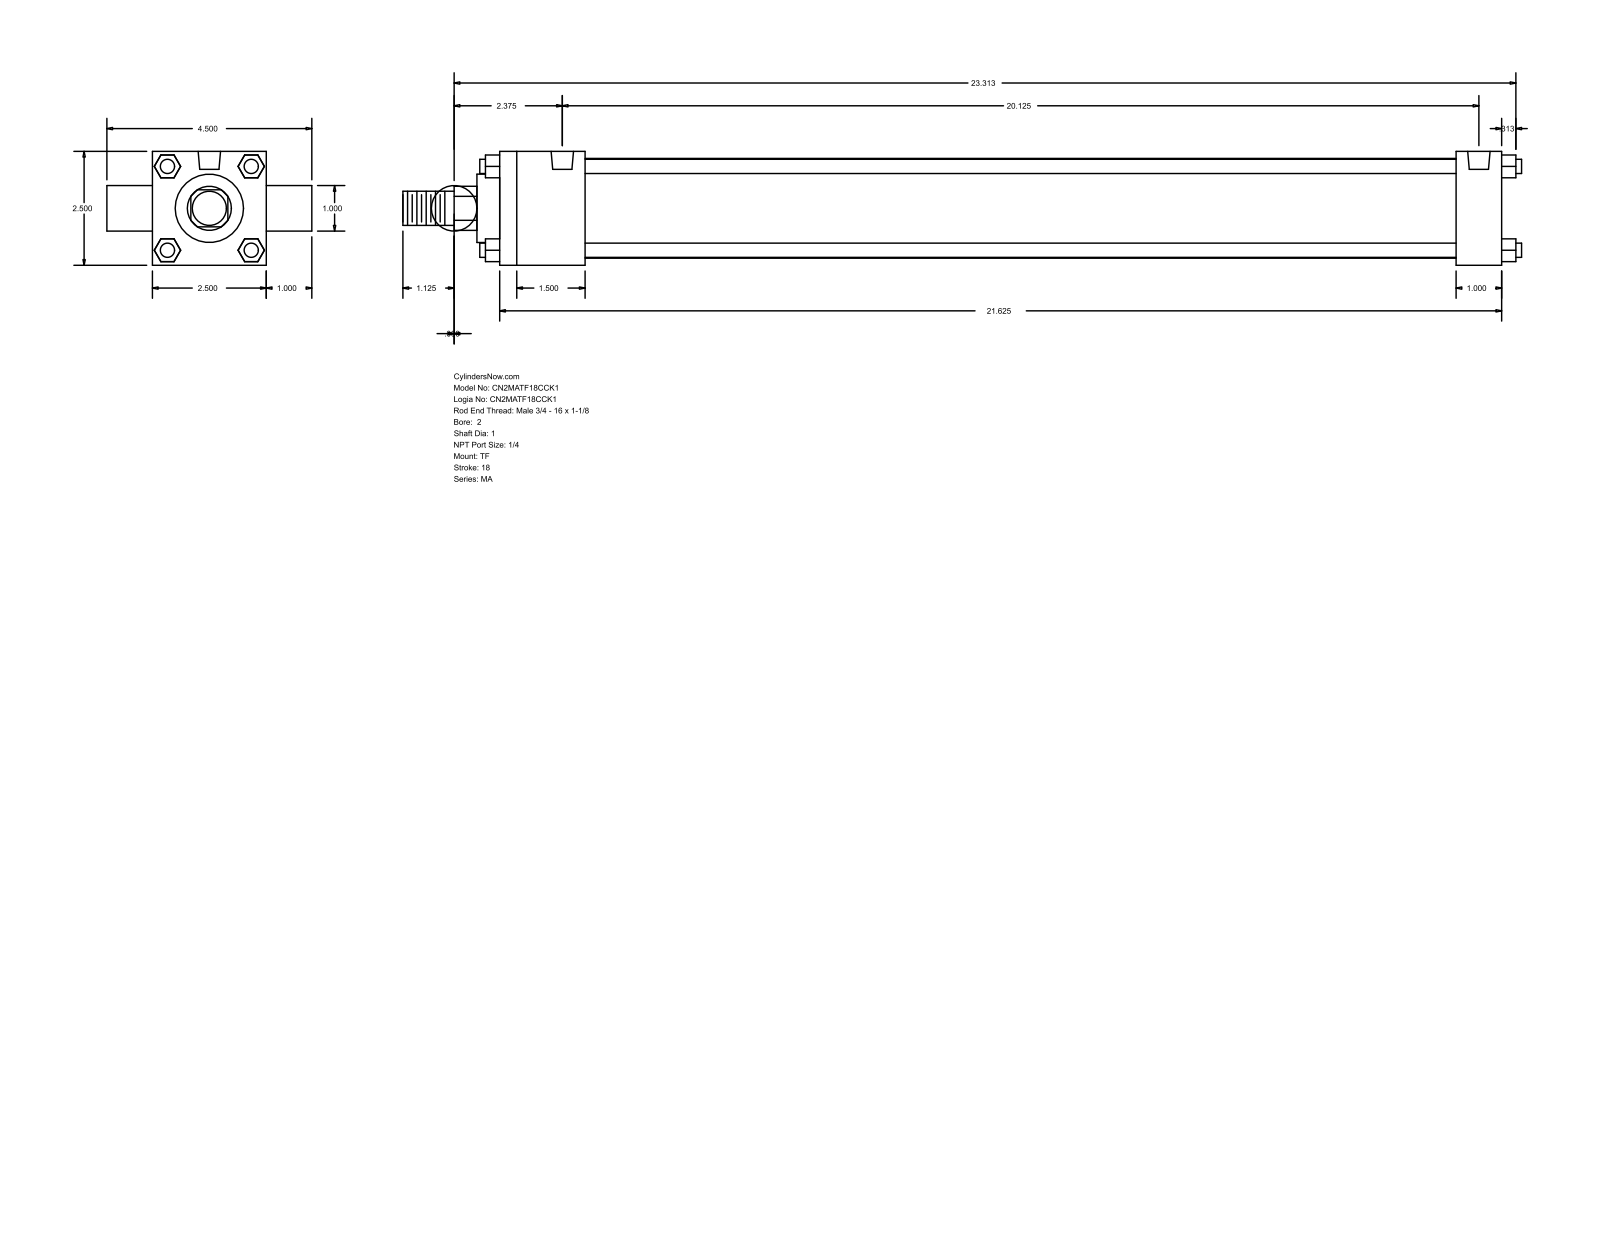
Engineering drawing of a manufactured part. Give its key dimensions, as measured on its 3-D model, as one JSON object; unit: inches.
{"part_name": "MA_TF__0200_1", "step_written_by": "GSSL Pune (CONFIG_CONTROL_DESIGN)", "units": "inches", "bodies": {"solids": 0, "faces": 120, "planar": 92, "cylindrical": 28, "other": 0}, "overall_size": [24.563, 4.5, 2.5], "round_holes": [[0.313, 3], [0.492, 2]], "round_bosses_or_shafts": [[0.313, 4], [1, 2], [2.19, 1], [1.5, 1], [0.75, 1]], "partial_cylinders_radius": [[0.484, 1]], "face_to_face_distances": [2.5, 1, 22, 0.5, 1.875, 21, 19.125, 20.125, 3.5, 1.593], "hole_center_spacings": [20.125]}
